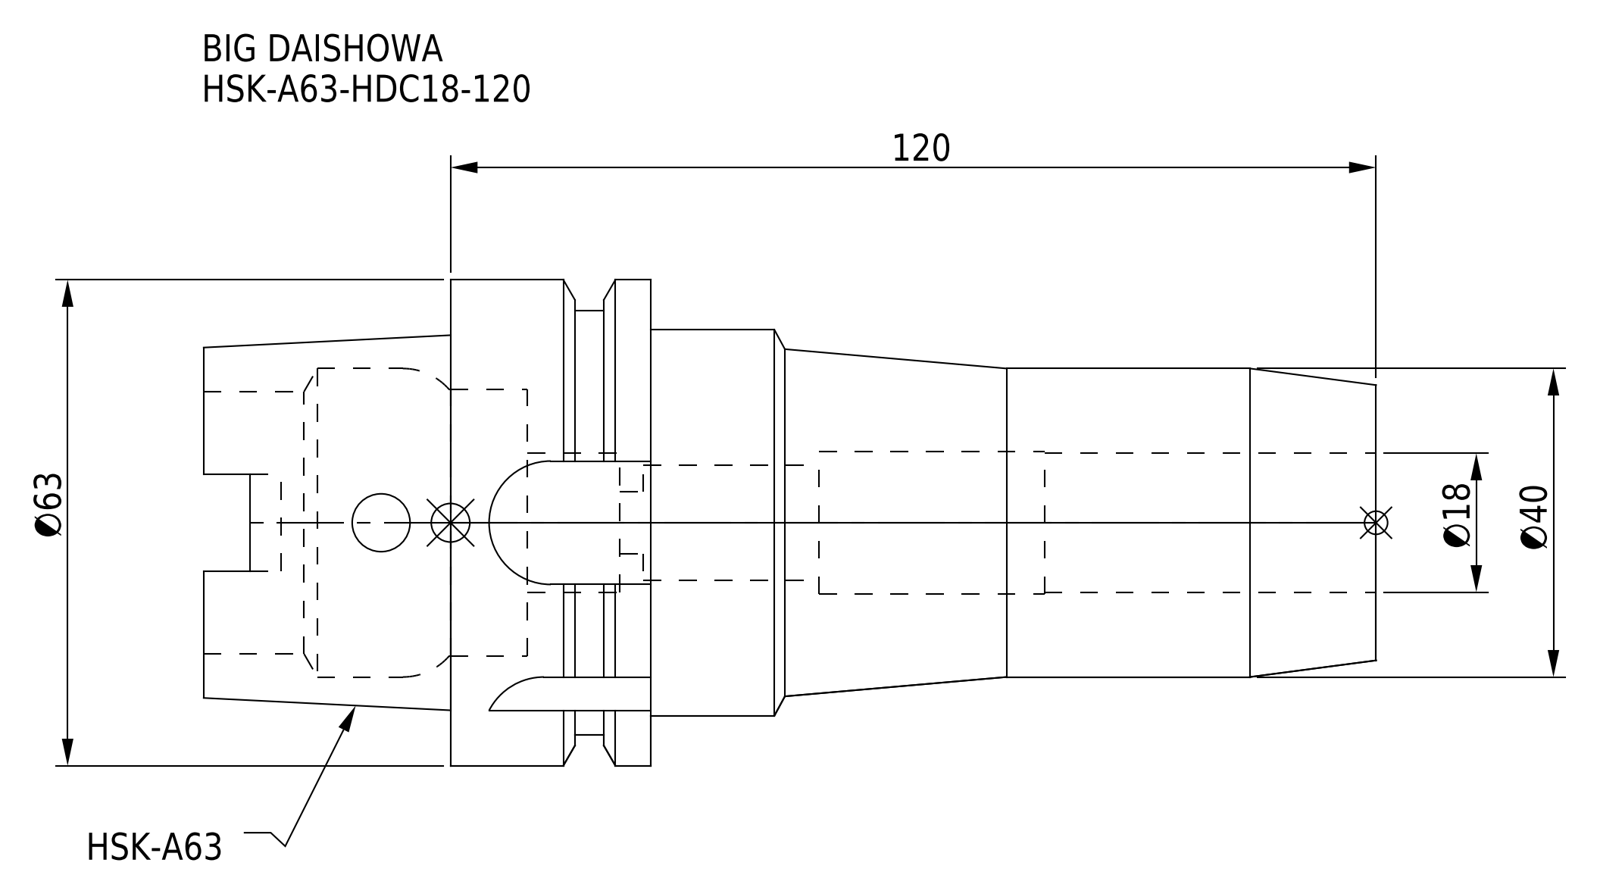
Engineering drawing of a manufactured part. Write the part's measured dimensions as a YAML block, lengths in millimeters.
part_name: "HSK-A63-HDC18-120"
step_written_by: "CREO PARAMETRIC BY PTC INC, 2016380 (AUTOMOTIVE_DESIGN)"
units: millimeters
bodies: {solids: 1, faces: 100, planar: 39, cylindrical: 41, other: 20}
overall_size: [152, 63, 63]
volume: 191564
surface_area: 39277
round_holes:
  - {diameter: 7.5, count: 1}
  - {diameter: 8, count: 1}
  - {diameter: 15, count: 1}
  - {diameter: 18, count: 1}
  - {diameter: 18.5, count: 1}
  - {diameter: 34, count: 1}
  - {diameter: 34.5, count: 1}
  - {diameter: 40, count: 1}
round_bosses_or_shafts:
  - {diameter: 63, count: 1}
  - {diameter: 55, count: 1}
  - {diameter: 50, count: 1}
partial_cylinders:
  - {radius: 2.88, count: 4}
  - {radius: 8, count: 4}
face_to_face_distances: [26, 94, 120, 110.05, 16.05, 9.95, 152, 58, 41.95, 32]
